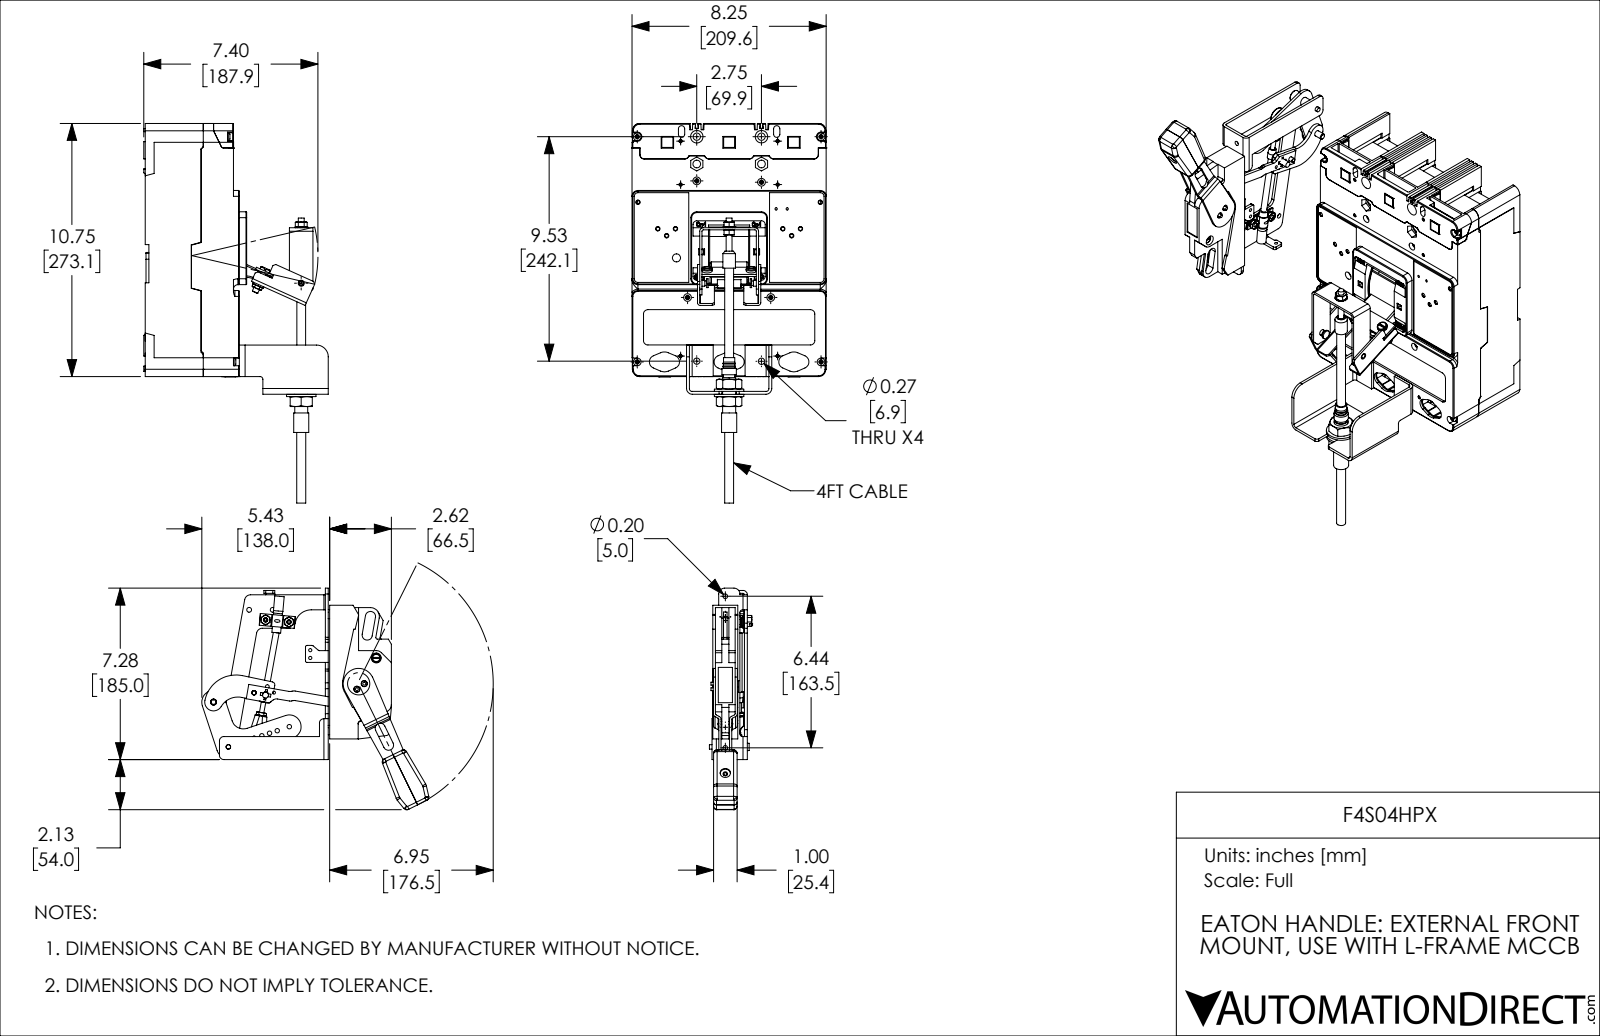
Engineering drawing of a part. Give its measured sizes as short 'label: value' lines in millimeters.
name: F4S04HPX; F4S04HPX_HANDLE; F4S04HPX_BREAKER
written by: SolidWorks 2019 (CONFIG_CONTROL_DESIGN)
unit: mm
bodies: 97 solids, 5868 faces (4033 planar, 1439 cylindrical, 396 other)
size: 415.5 × 365.9 × 245.1
volume: 3 921 000 mm³; area: 767 100 mm²
holes: 13× ⌀4.8, 10× ⌀4.3, 8× ⌀3.7, 7× ⌀8.3, 6× ⌀2.8, 6× ⌀3.6, 6× ⌀4.8, 6× ⌀5.2, 6× ⌀13.5, 4× ⌀3.7, 4× ⌀5.5, 4× ⌀6.4
bosses: 11× ⌀6.4, 6× ⌀9.5, 6× ⌀7.4, 4× ⌀12.7, 3× ⌀8.3, 3× ⌀7.9, 2× ⌀11.9, 2× ⌀10.8
rounds: 70× R1.6, 53× R0.8, 52× R6.4, 40× R3.2, 32× R0.8, 30× R4.8, 28× R1.5, 18× R4
face distances: 61.9, 209.6, 6.4, 94.4, 32.5, 3.2, 69.9, 2.4, 100.8, 38.9
hole spacings: 134.1, 69.9, 198.5, 134.2, 242.9, 64.3, 243, 64.3
